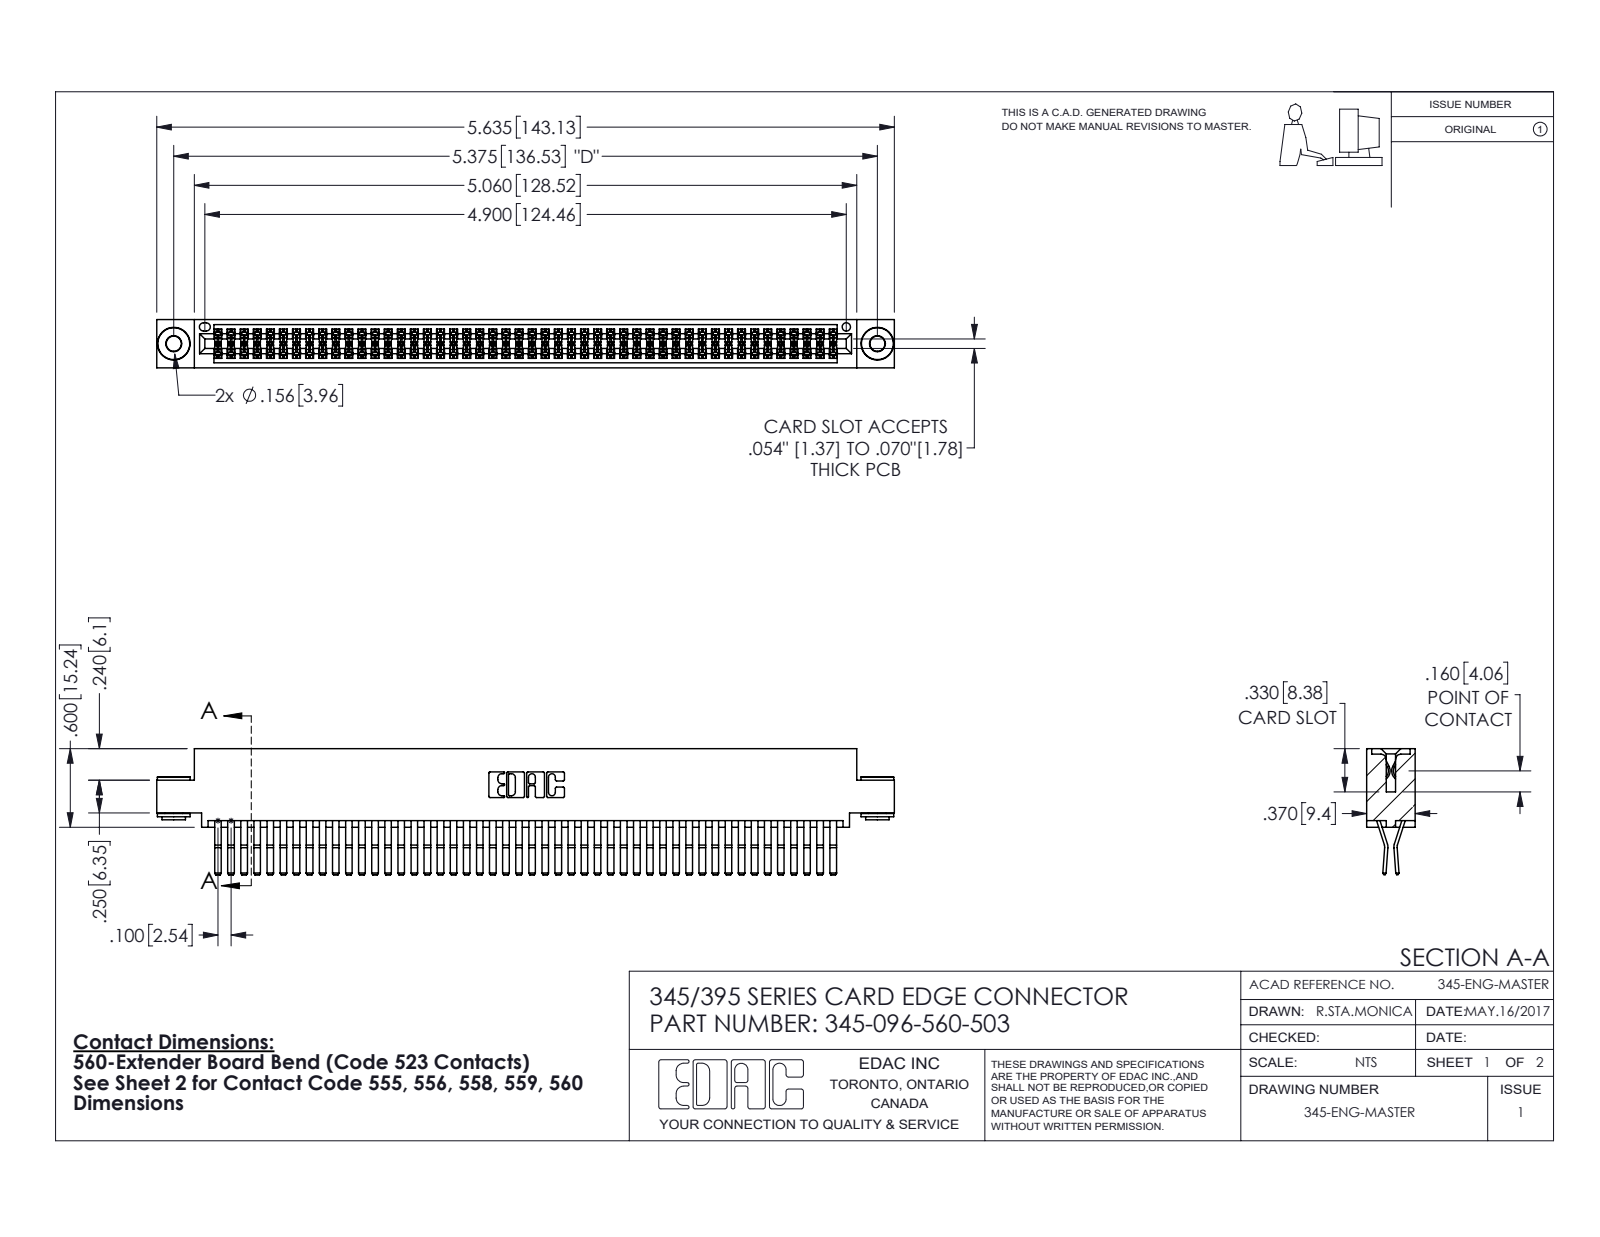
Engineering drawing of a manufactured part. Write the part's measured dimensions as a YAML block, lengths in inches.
part_name: "345-096-560-503; 345-250-002_345-250-002-102; 345-292-001_560 Tail; 345 Part_0.110 Offset - 0.156 Dia-TH"
step_written_by: "SolidWorks 2016 (CONFIG_CONTROL_DESIGN)"
units: inches
bodies: {solids: 99, faces: 5160, planar: 3262, cylindrical: 1890, other: 8}
overall_size: [5.635, 0.962, 0.37]
volume: 0.887
surface_area: 36.45
round_holes:
  - {diameter: 0.116, count: 2}
  - {diameter: 0.156, count: 2}
  - {diameter: 0.064, count: 1}
round_bosses_or_shafts:
  - {diameter: 0.25, count: 2}
  - {diameter: 0.18, count: 2}
  - {diameter: 0.136, count: 2}
partial_cylinders:
  - {radius: 0.006, count: 144}
  - {radius: 0.01, count: 22}
  - {radius: 0.007, count: 6}
  - {radius: 0.031, count: 6}
  - {radius: 0.026, count: 3}
  - {radius: 0.01, count: 2}
  - {radius: 0.014, count: 2}
  - {radius: 0.019, count: 2}
face_to_face_distances: [0.025, 0.072, 0.298, 0.37, 0.2, 0.098, 0.272, 0.225, 0.175, 0.149]
hole_center_spacings: [0.27, 5.139, 5.375]
